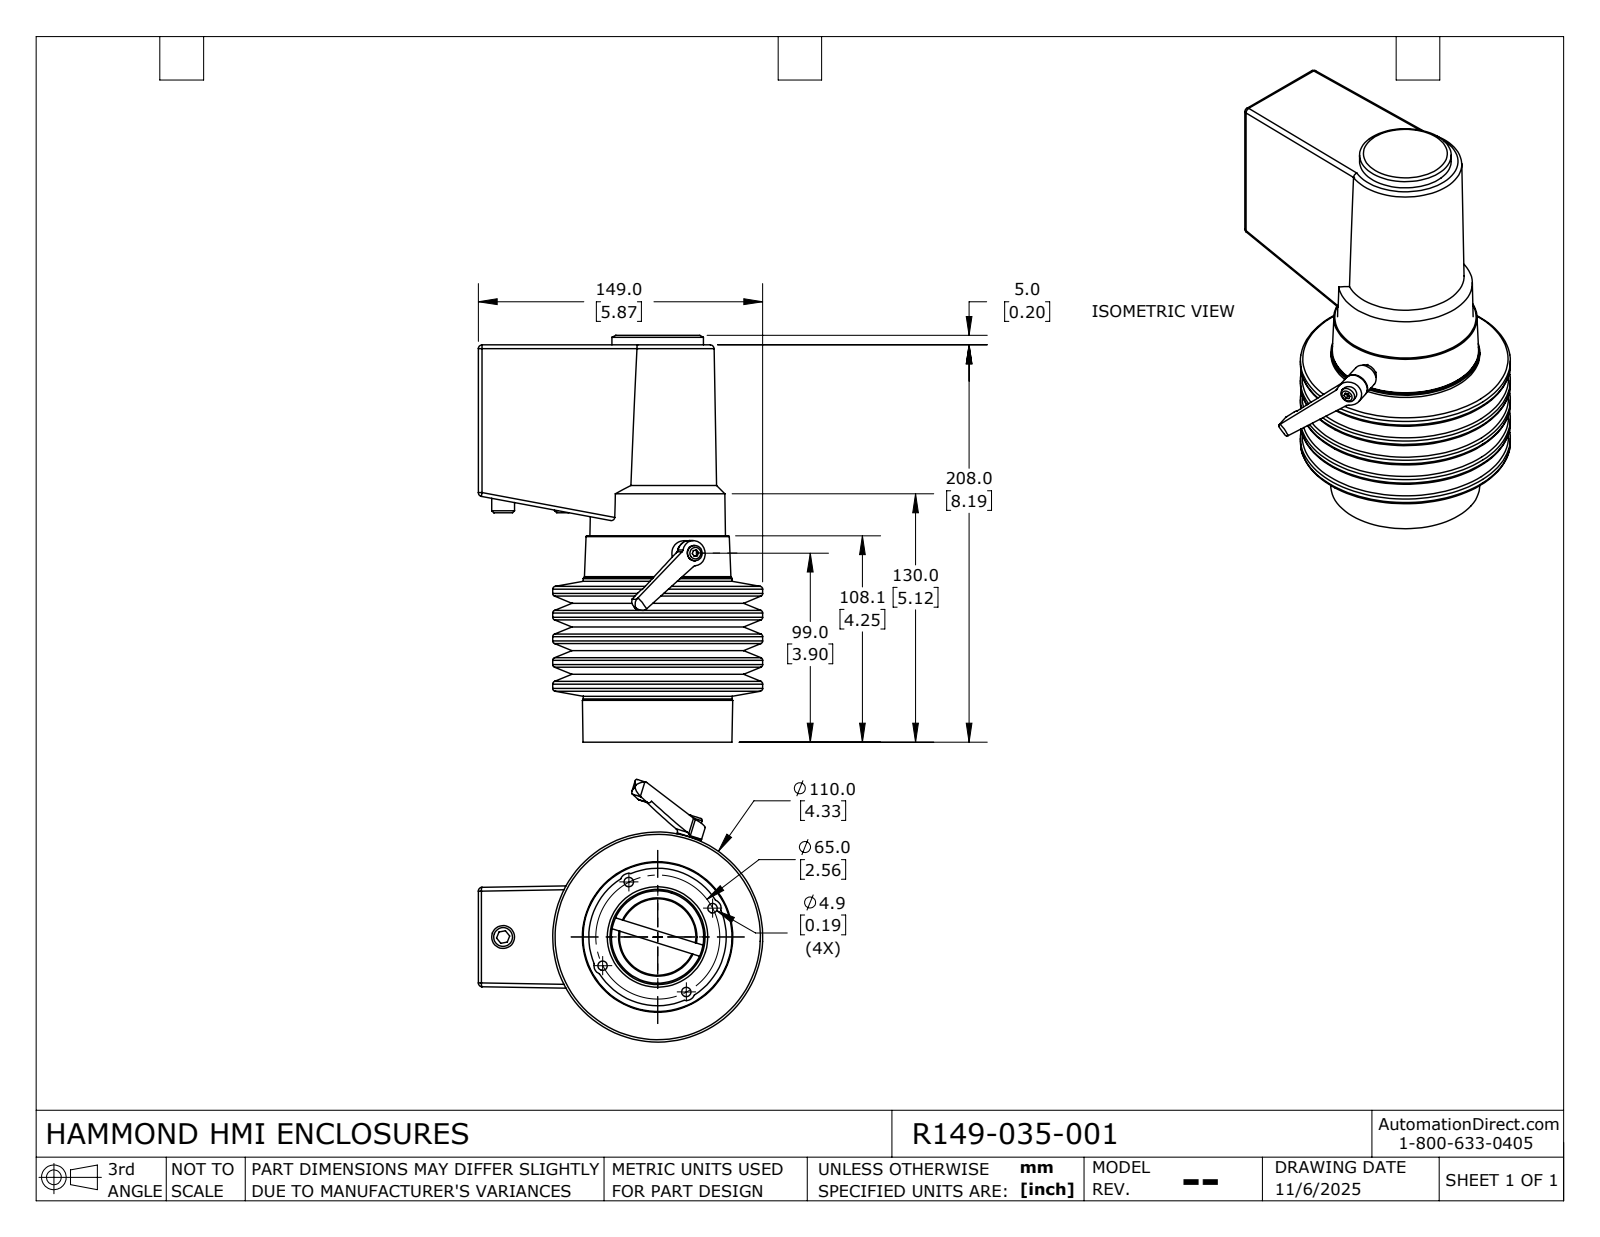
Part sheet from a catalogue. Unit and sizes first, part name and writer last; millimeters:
Units: millimetres
Overall size (bounding box): 337 × 213 × 137.52
Round holes (diameter × count): ⌀4.92 ×4, ⌀6 ×2, ⌀10.11 ×2, ⌀72 ×2, ⌀4.92 ×1, ⌀40 ×1, ⌀48.38 ×1, ⌀51 ×1, ⌀52.6 ×1, ⌀86 ×1, ⌀106 ×1
Round bosses / shafts (diameter × count): ⌀86 ×2, ⌀12 ×2, ⌀6 ×2, ⌀110 ×1, ⌀78 ×1, ⌀70.25 ×1, ⌀51 ×1, ⌀48 ×1
Partial cylindrical surfaces — rounded edges, fillets, slot ends (radius × count): R0.3 ×56, R2 ×38, R4 ×8, R0.5 ×6, R4.5 ×4, R5 ×4, R4 ×1, R6.6 ×1
Main face-to-face distances: 3, 37, 57, 40, 34, 60, 54, 14.9, 71.9, 68.9
Hole centre spacings: 32.5, 45.96, 32.43, 32.57, 65, 24.31, 32.38, 32.48
Volume: 699 319 mm³ · Surface area: 316 655 mm²
Bodies: 11 solids, 471 faces (121 planar, 179 cylindrical, 171 other)
Part name (STEP PRODUCT): R149-035-001
STEP written by: SolidWorks 2024 (AUTOMOTIVE_DESIGN)
